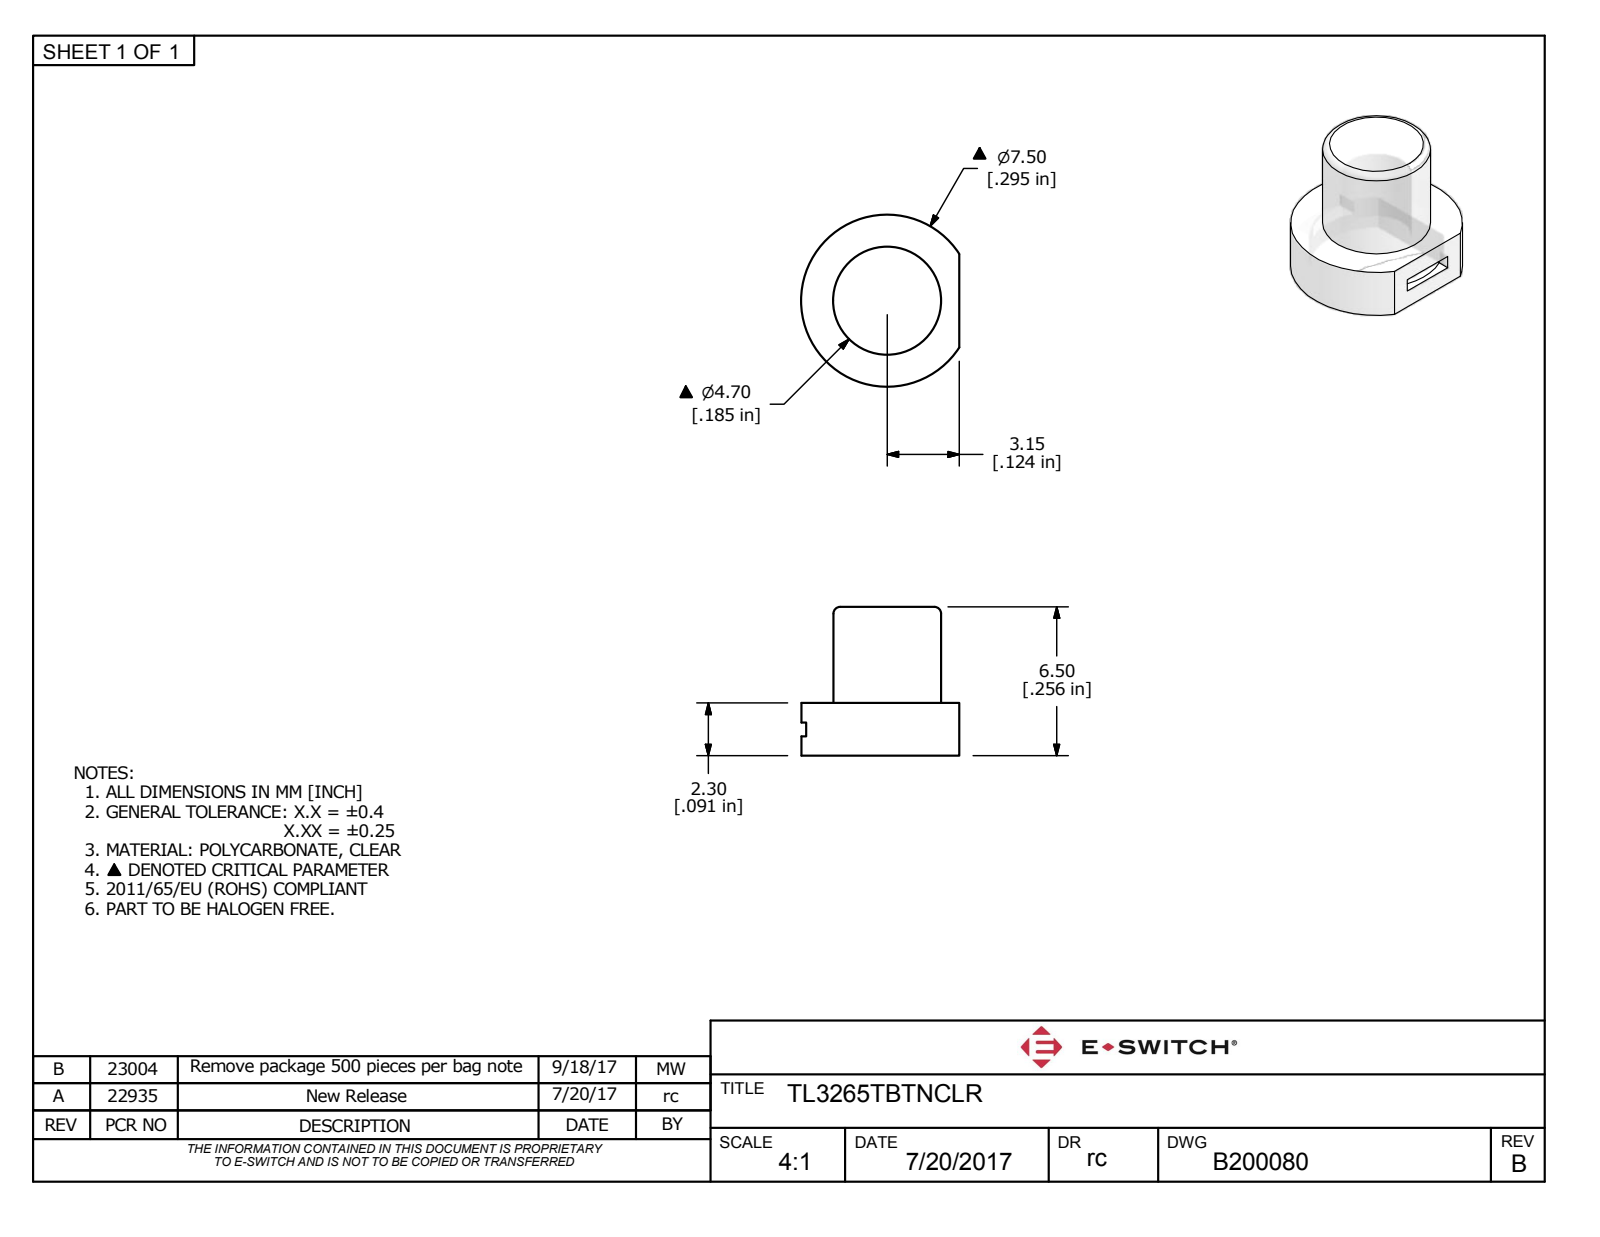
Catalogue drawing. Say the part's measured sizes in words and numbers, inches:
The part is named "TL3265TBTNCLR". Its 3-D file was written by "Autodesk Inventor 2022 (AUTOMOTIVE_DESIGN)". It is 1 solid with 22 faces: 16 planar, 5 cylindrical and 1 other. Overall it measures 0.295 by 0.272 by 0.256 inches. Its volume is 0.007 cubic inches and its surface area 0.401 square inches. Round holes: 1 of diameter 0.118. Round bosses or shafts: 1 of diameter 0.295, 1 of diameter 0.185. Partial cylindrical surfaces (rounded edges, fillets, slot ends): 1 of radius 0.114. The main face-to-face distances are 0.063, 0.091, 0.193, 0.165, 0.028, 0.256, 0.033, 0.13, 0.102, 0.057.
